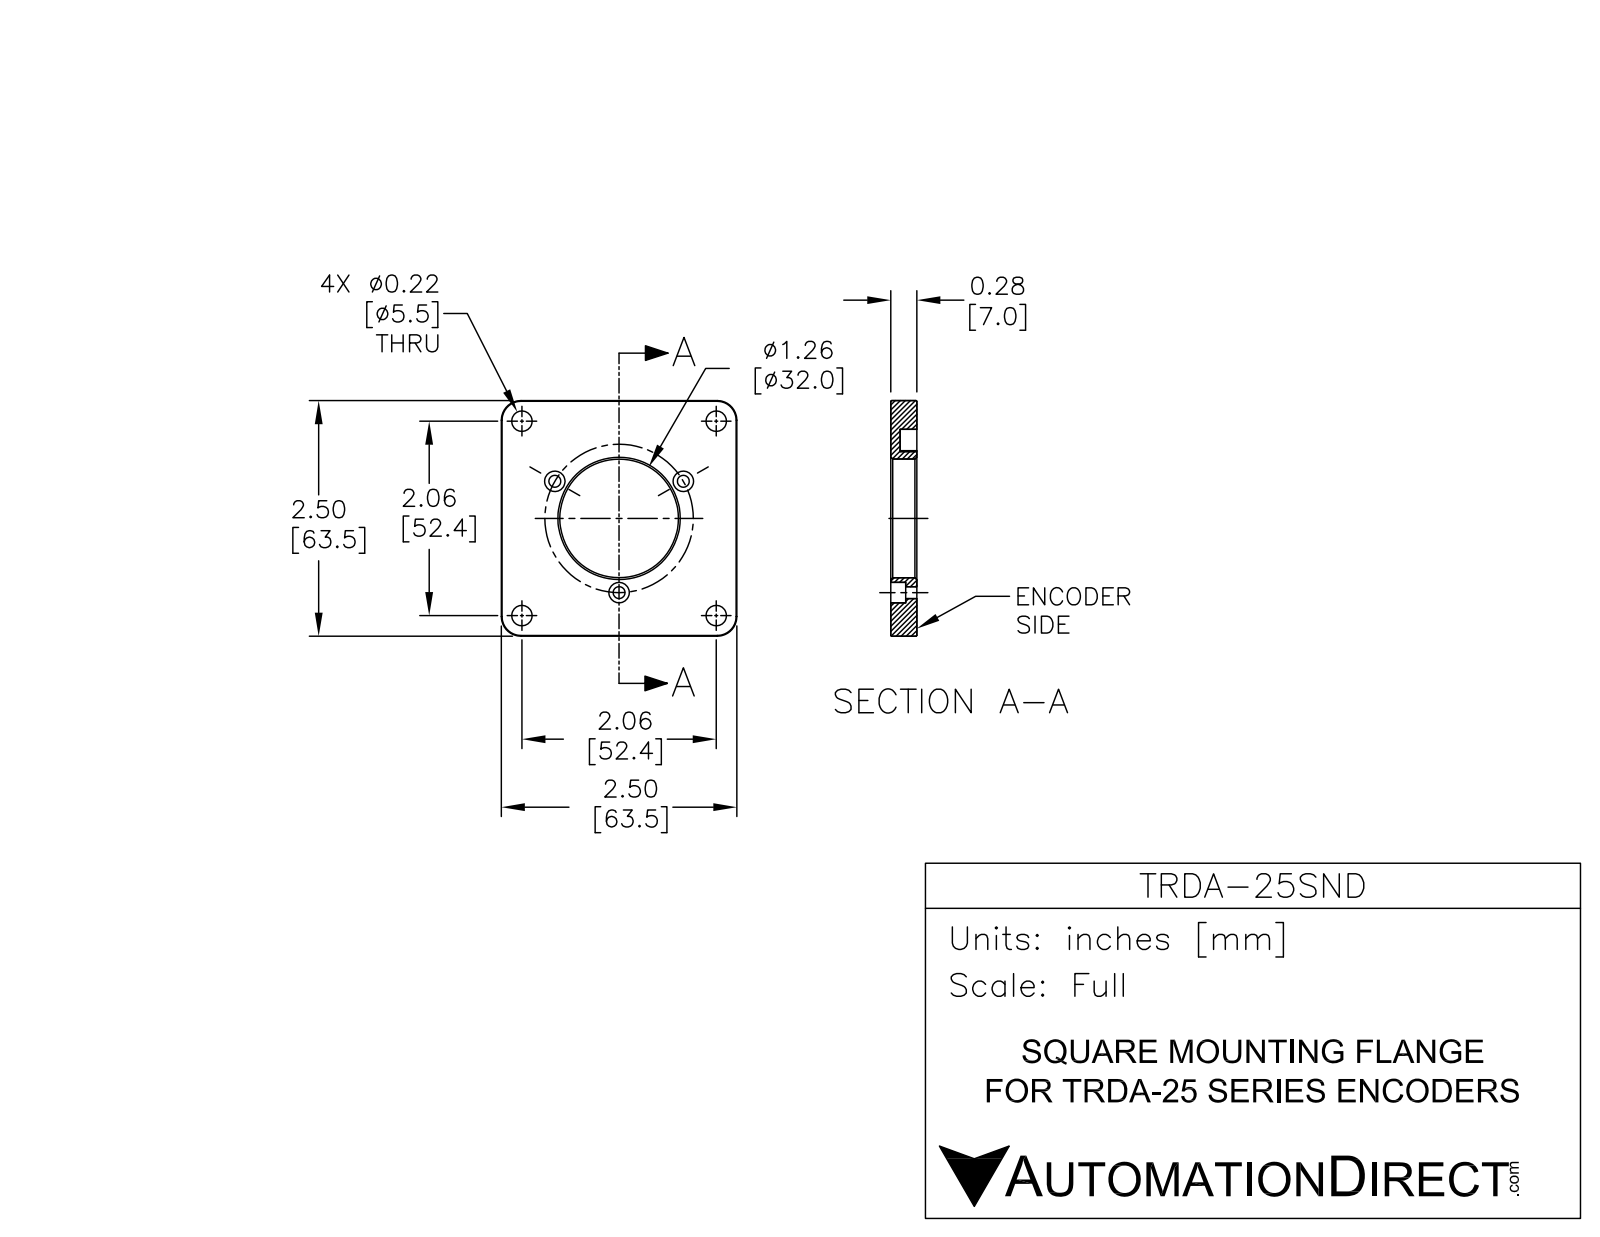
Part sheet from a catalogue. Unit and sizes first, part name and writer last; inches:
Units: inches
Overall size (bounding box): 2.5 × 2.5 × 0.276
Round holes (diameter × count): ⌀0.217 ×7, ⌀0.126 ×3, ⌀1.26 ×1
Partial cylindrical surfaces — rounded edges, fillets, slot ends (radius × count): R0.039 ×12, R0.209 ×4, R0.709 ×1, R0.945 ×1
Main face-to-face distances: 0.276, 2.5, 0.177, 0.098, 1.951, 0.118, 0.059, 0.157
Hole centre spacings: 1.459, 2.063, 0.787, 1.364, 0.727, 1.06, 1.467, 1.828
Volume: 1.149 in³ · Surface area: 15.88 in²
Bodies: 1 solid, 88 faces (26 planar, 50 cylindrical, 12 other)
Part name (STEP PRODUCT): TRDA-25SND
STEP written by: SolidWorks 2016 (AUTOMOTIVE_DESIGN)
